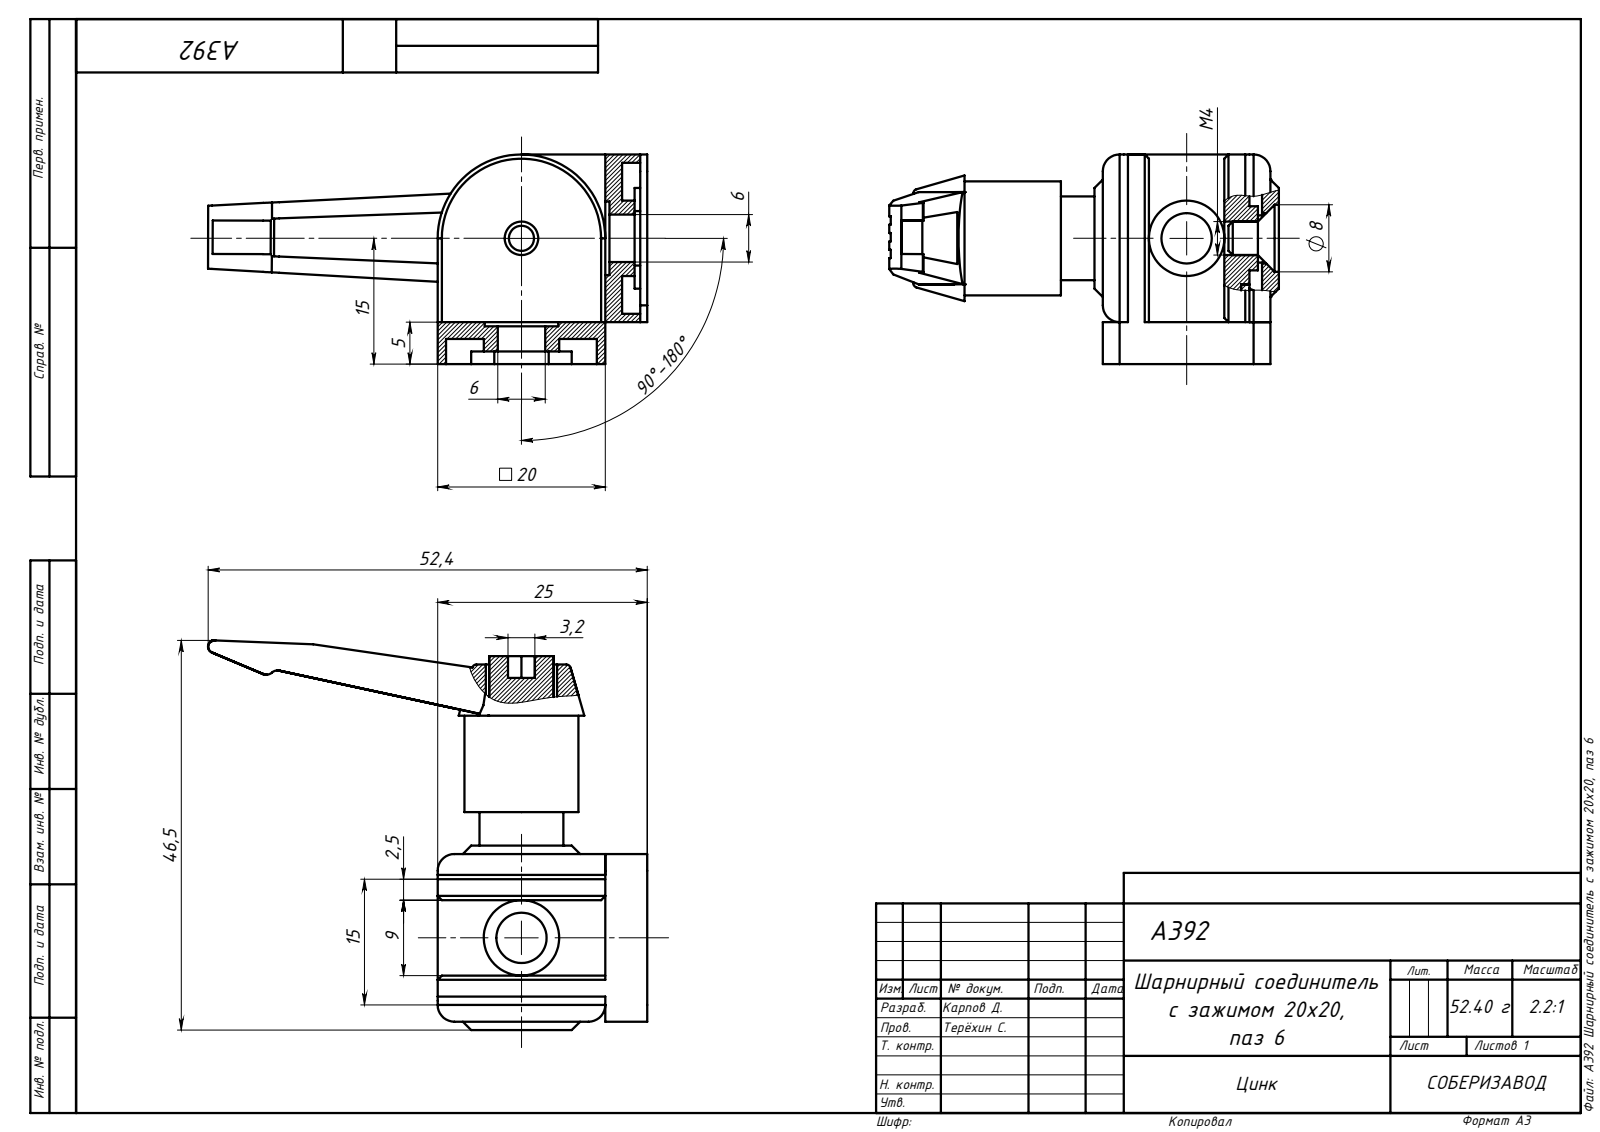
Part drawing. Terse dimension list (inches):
name: A392 Шарнирный соединитель с зажимом 20х20, паз 6_00; A392 Втулка_00; A392 Ручка_11; A392 Шайба (+2 more)
written by: SolidWorks 2020 (AUTOMOTIVE_DESIGN)
unit: in
bodies: 10 solids, 330 faces (215 planar, 79 cylindrical, 36 other)
size: 2.063 × 1.83 × 0.984
volume: 0.63 in³; area: 16.25 in²
holes: 2× ⌀0.236, 2× ⌀0.354, 1× ⌀0.157, 1× ⌀0.335, 1× ⌀0.433, 1× ⌀0.669
bosses: 1× ⌀0.551, 1× ⌀0.535, 1× ⌀0.394, 1× ⌀0.315, 1× ⌀0.303, 1× ⌀0.236
rounds: 8× R0.079, 2× R0.039, 1× R0.03, 1× R0.394
face distances: 0.118, 0.079, 0.098, 0.039, 0.571, 0.138, 0.02, 0.689, 0.551, 0.65
